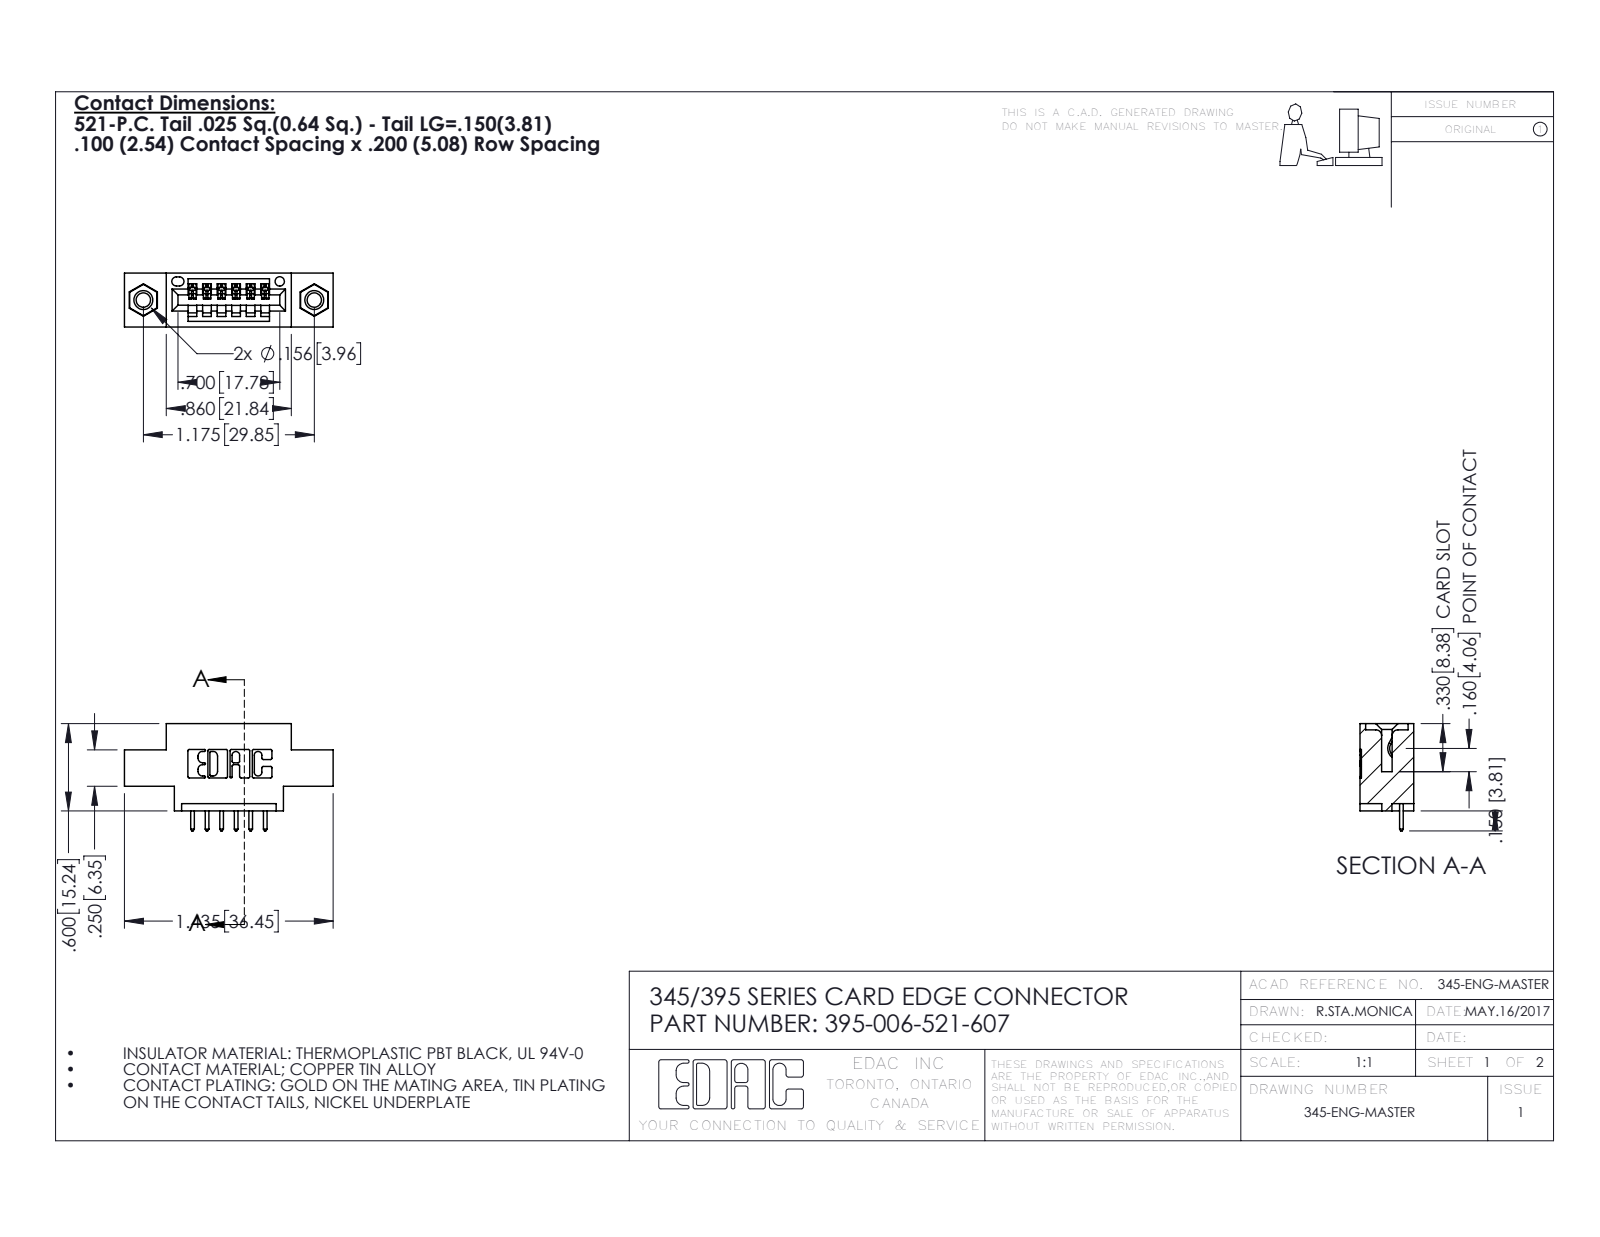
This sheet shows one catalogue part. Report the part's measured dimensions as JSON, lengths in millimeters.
{"part_name": "345 Part_0.170 Offset - 0.156 Dia-TI; 395-006-521-607; 345-250-001_345-250-005-103; 345-292-001_345-293-121", "step_written_by": "SolidWorks 2016 (CONFIG_CONTROL_DESIGN)", "units": "millimeters", "bodies": {"solids": 9, "faces": 538, "planar": 356, "cylindrical": 166, "other": 16}, "overall_size": [36.4, 18.7, 9.4], "volume_mm3": 3020, "surface_area_mm2": 3621, "round_holes": [[2.5, 2], [3.2, 2], [4, 2], [1.6, 1]], "round_bosses_or_shafts": [[3.9, 2]], "partial_cylinders_radius": [[0.3, 22], [0.2, 12], [0.3, 12], [0.2, 6], [0.8, 6], [0.7, 3], [0.8, 2], [1, 2]], "face_to_face_distances": [9.4, 5.1, 2.5, 1.8, 7.6, 0.6, 2.5, 6.9, 1.5, 7.6], "hole_center_spacings": [6.9, 24, 29.8]}
